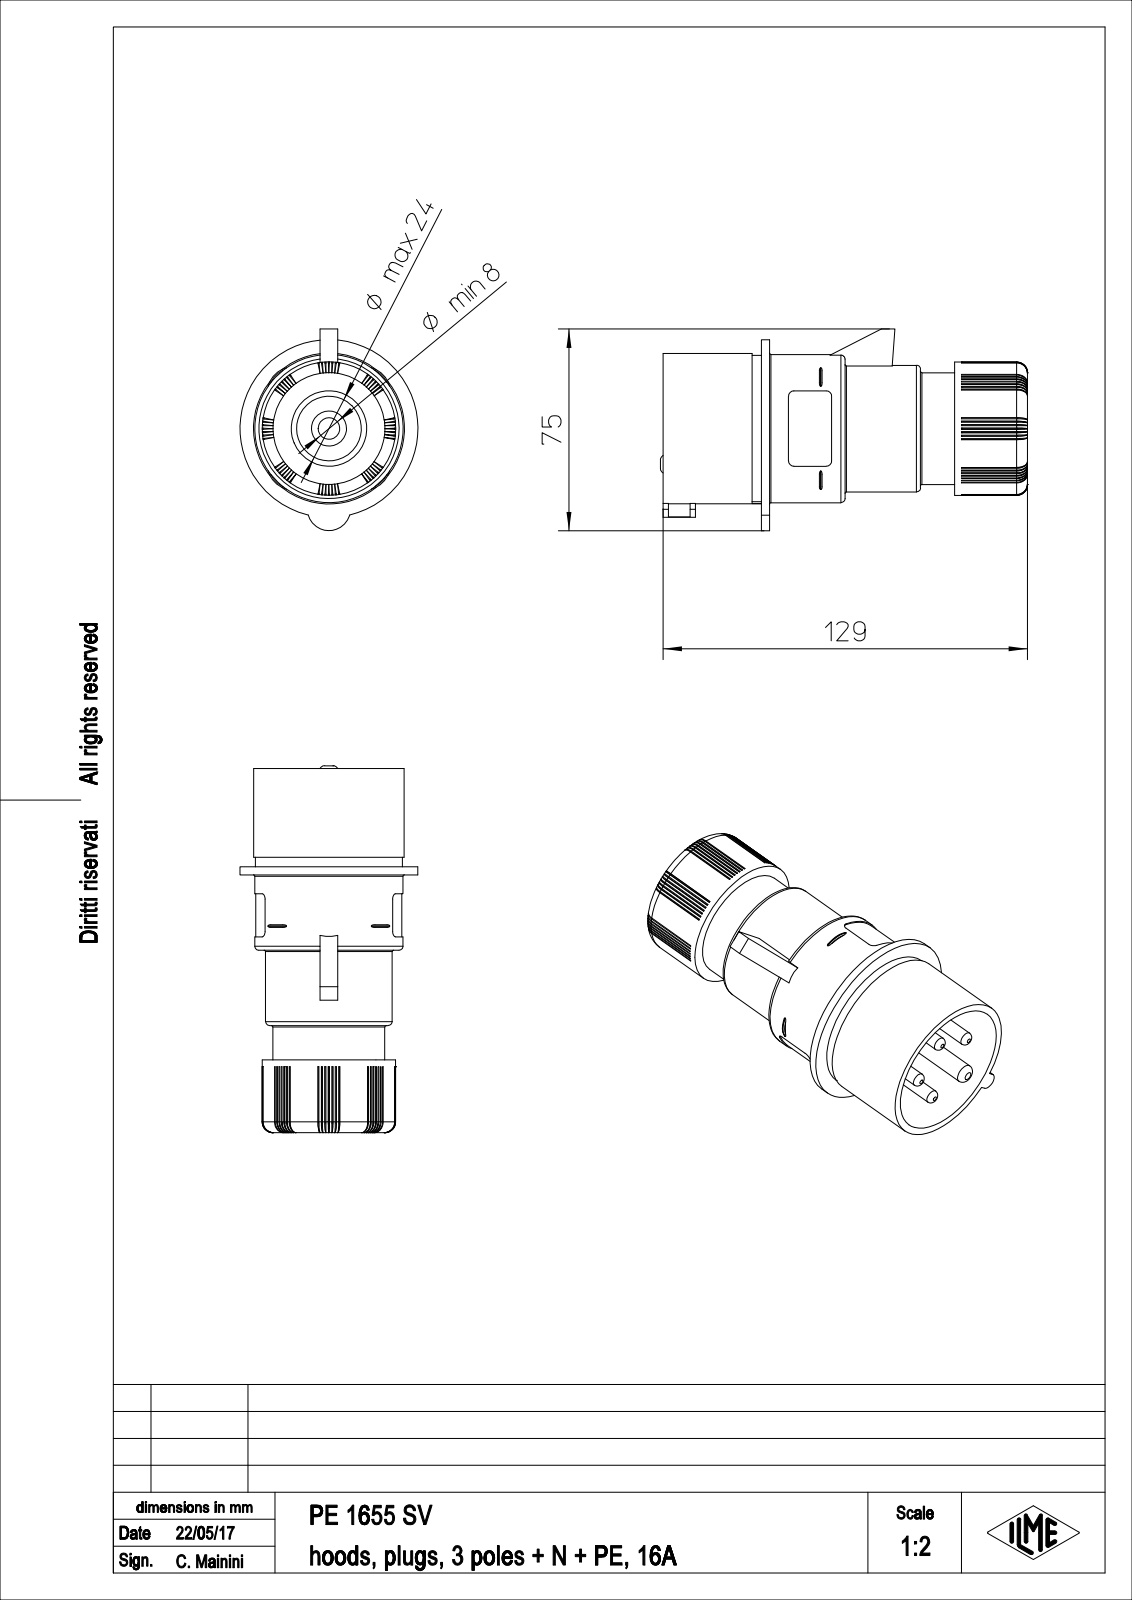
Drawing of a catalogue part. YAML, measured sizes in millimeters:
part_name: "PE_1655_SV"
step_written_by: "PTC Creo Elements/Direct Modeling 19.0E 27-Jun-2016 (C) Parametric Technology GmbH (AUTOMOTIVE_DESIGN)"
units: millimeters
bodies: {solids: 1, faces: 635, planar: 273, cylindrical: 110, other: 252}
overall_size: [136.2, 74.9, 66]
volume: 186671
surface_area: 55541
round_holes:
  - {diameter: 19, count: 1}
  - {diameter: 24, count: 1}
  - {diameter: 25, count: 1}
  - {diameter: 32, count: 1}
round_bosses_or_shafts:
  - {diameter: 5, count: 4}
  - {diameter: 6.7, count: 2}
  - {diameter: 66, count: 1}
  - {diameter: 55.8, count: 1}
  - {diameter: 55, count: 1}
  - {diameter: 54.5, count: 1}
  - {diameter: 49.5, count: 1}
  - {diameter: 49, count: 1}
partial_cylinders:
  - {radius: 3.6, count: 56}
  - {radius: 2, count: 4}
  - {radius: 10, count: 4}
  - {radius: 4, count: 2}
  - {radius: 3, count: 1}
  - {radius: 8, count: 1}
  - {radius: 27.1, count: 1}
face_to_face_distances: [3, 95.7, 98.7, 71.7, 68.7, 27, 36.5, 39.5, 108.2, 135.2]
